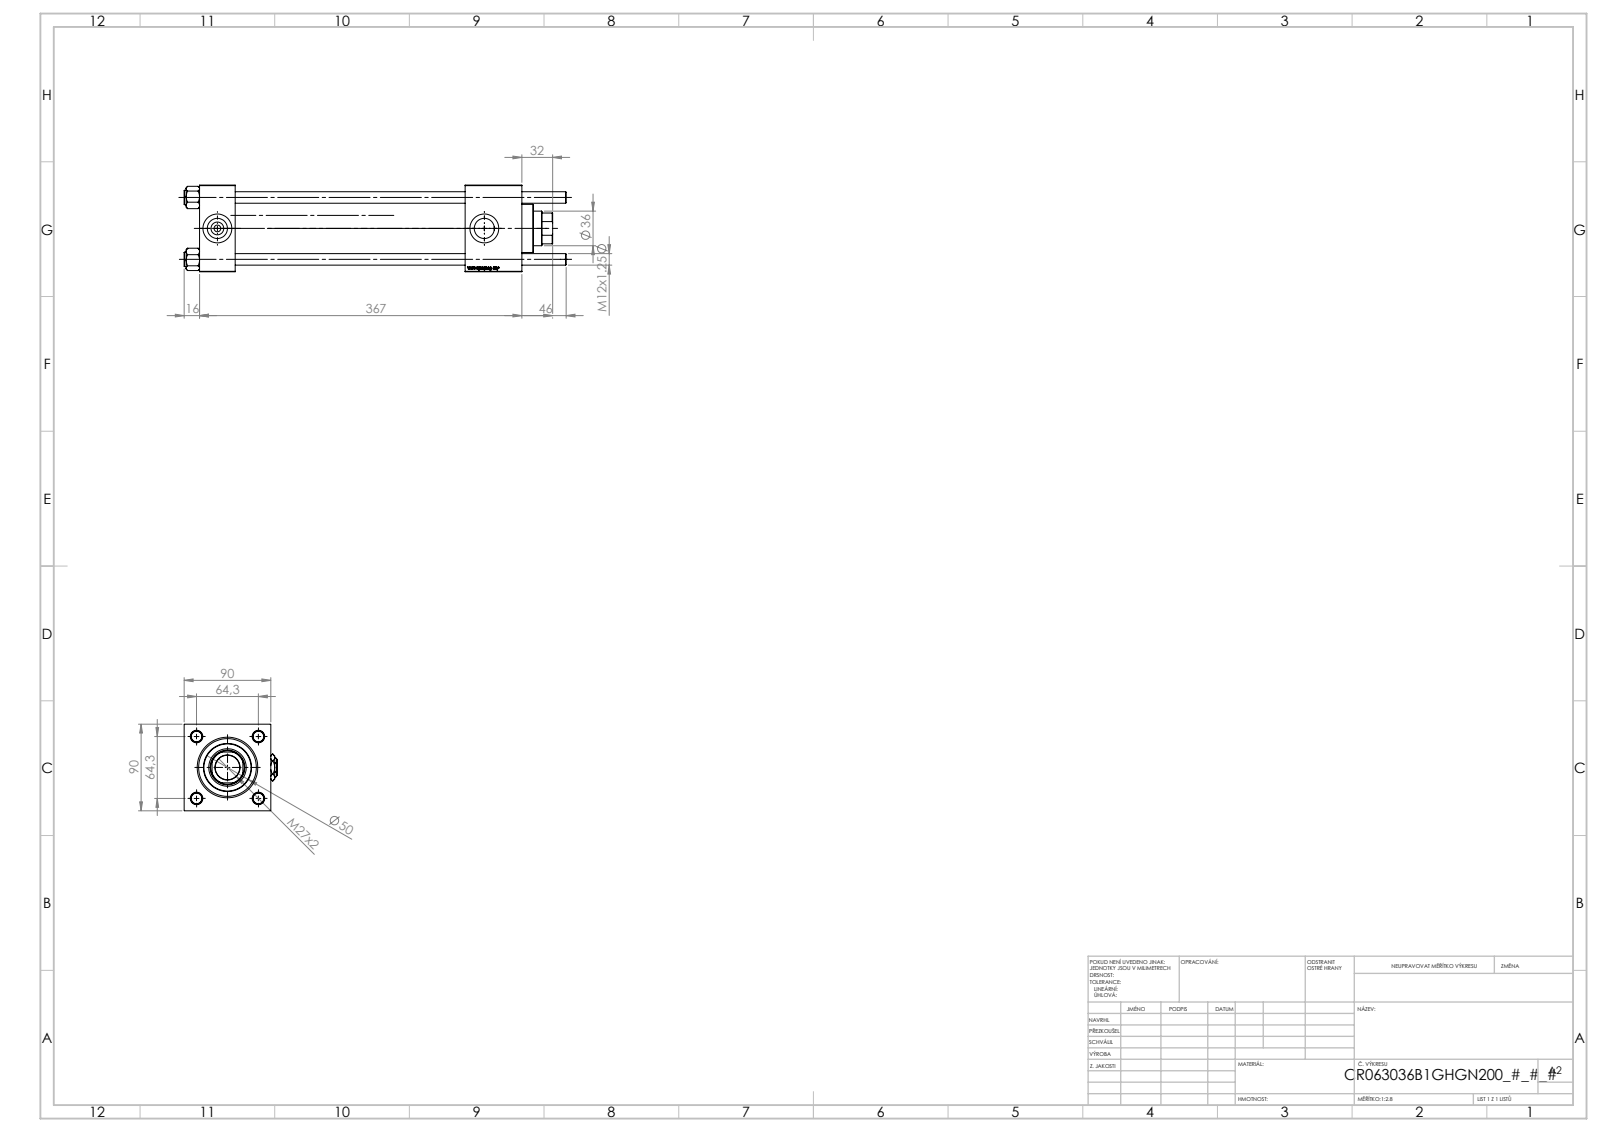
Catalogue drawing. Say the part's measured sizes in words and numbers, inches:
The part is named "V215CR_VCP_B; V215_VC_A; Zatka_pro_OIL_PORT; V215CR_B-1 (+2 more)". Its 3-D file was written by "SolidWorks 2019 (CONFIG_CONTROL_DESIGN)". It is 12 solids with 1205 faces: 455 planar, 82 cylindrical and 668 other. Overall it measures 15.63 by 3.819 by 3.543 inches. Its volume is 83.91 cubic inches and its surface area 502.8 square inches. Round holes: 4 of diameter 0.472, 2 of diameter 0.276, 2 of diameter 0.825, 2 of diameter 1.181, 1 of diameter 1.004, 1 of diameter 1.417, 1 of diameter 1.535, 1 of diameter 1.969, 1 of diameter 2.362, 1 of diameter 2.48. Round bosses or shafts: 4 of diameter 0.591, 1 of diameter 2.717. Partial cylindrical surfaces (rounded edges, fillets, slot ends): 1 of radius 0.689. The main face-to-face distances are 3.543, 1.457, 11.732, 13.189, 2.323, 10.866, 9.409, 12.059, 10.602, 1.193. The hole center spacings are 1.79, 2.531, 3.58, 10.925.
